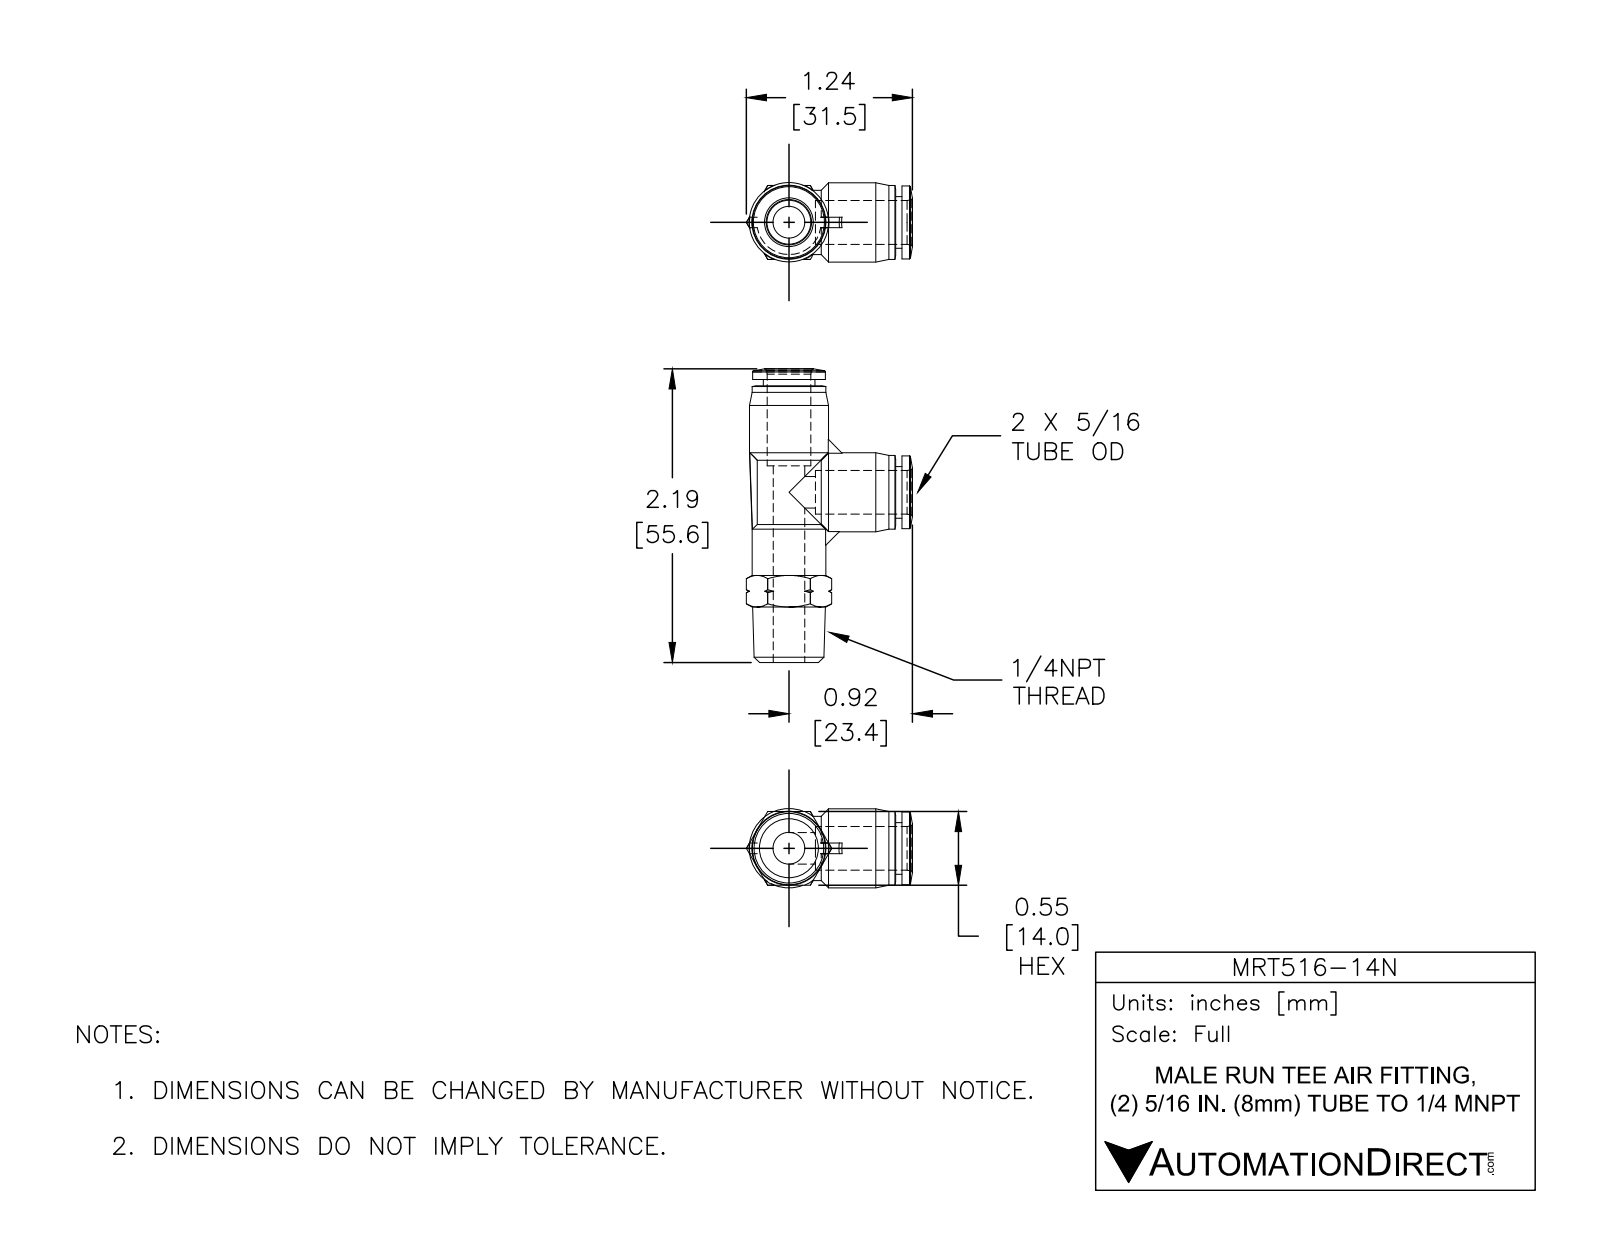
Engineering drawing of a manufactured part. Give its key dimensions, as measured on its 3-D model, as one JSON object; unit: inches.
{"part_name": "MRT516-14N", "step_written_by": "SolidWorks 2015 (CONFIG_CONTROL_DESIGN)", "units": "inches", "bodies": {"solids": 1, "faces": 116, "planar": 22, "cylindrical": 30, "other": 64}, "overall_size": [2.191, 1.239, 0.591], "volume_in3": 0.484, "surface_area_in2": 8.493, "round_holes": [[0.236, 2], [0.327, 2]], "round_bosses_or_shafts": [[0.591, 2], [0.551, 2], [0.543, 2], [0.48, 2], [0.386, 2]], "face_to_face_distances": [0.551, 0.047, 2.112, 0.598, 0.646, 2.065, 0.236, 0.315, 1.467, 0.079]}
